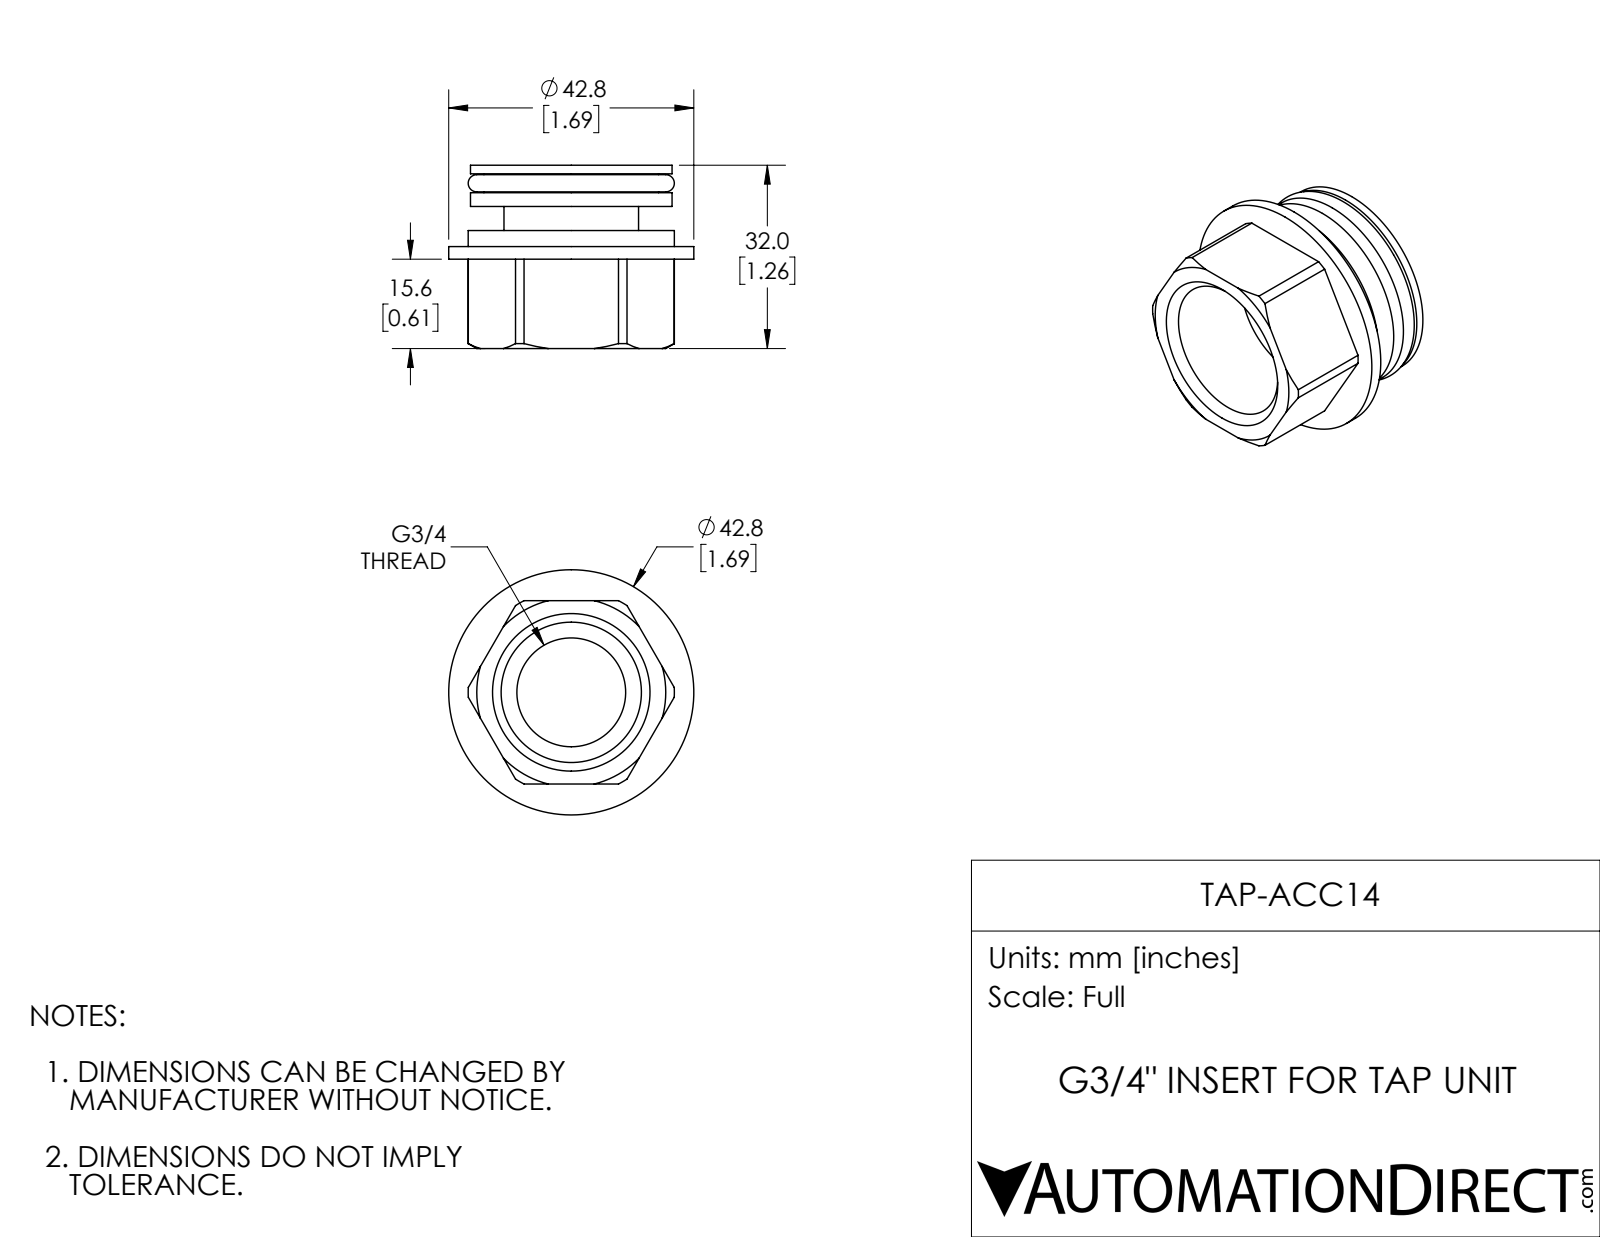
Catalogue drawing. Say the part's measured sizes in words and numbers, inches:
The part is named "TAP-ACC14". Its 3-D file was written by "SolidWorks 2017 (AUTOMOTIVE_DESIGN)". It is 1 solid with 56 faces: 14 planar, 26 cylindrical and 16 other. Overall it measures 1.685 by 1.685 by 1.26 inches. Its volume is 0.923 cubic inches and its surface area 15.33 square inches. Round holes: 1 of diameter 0.748, 1 of diameter 0.965, 1 of diameter 1.024. Round bosses or shafts: 1 of diameter 1.685, 1 of diameter 1.417, 1 of diameter 1.386, 1 of diameter 1.201, 1 of diameter 0.925. The main face-to-face distances are 1.26, 0.197, 0.362, 0.165, 0.646, 0.449, 0.283, 0.087, 0.11, 0.276.
